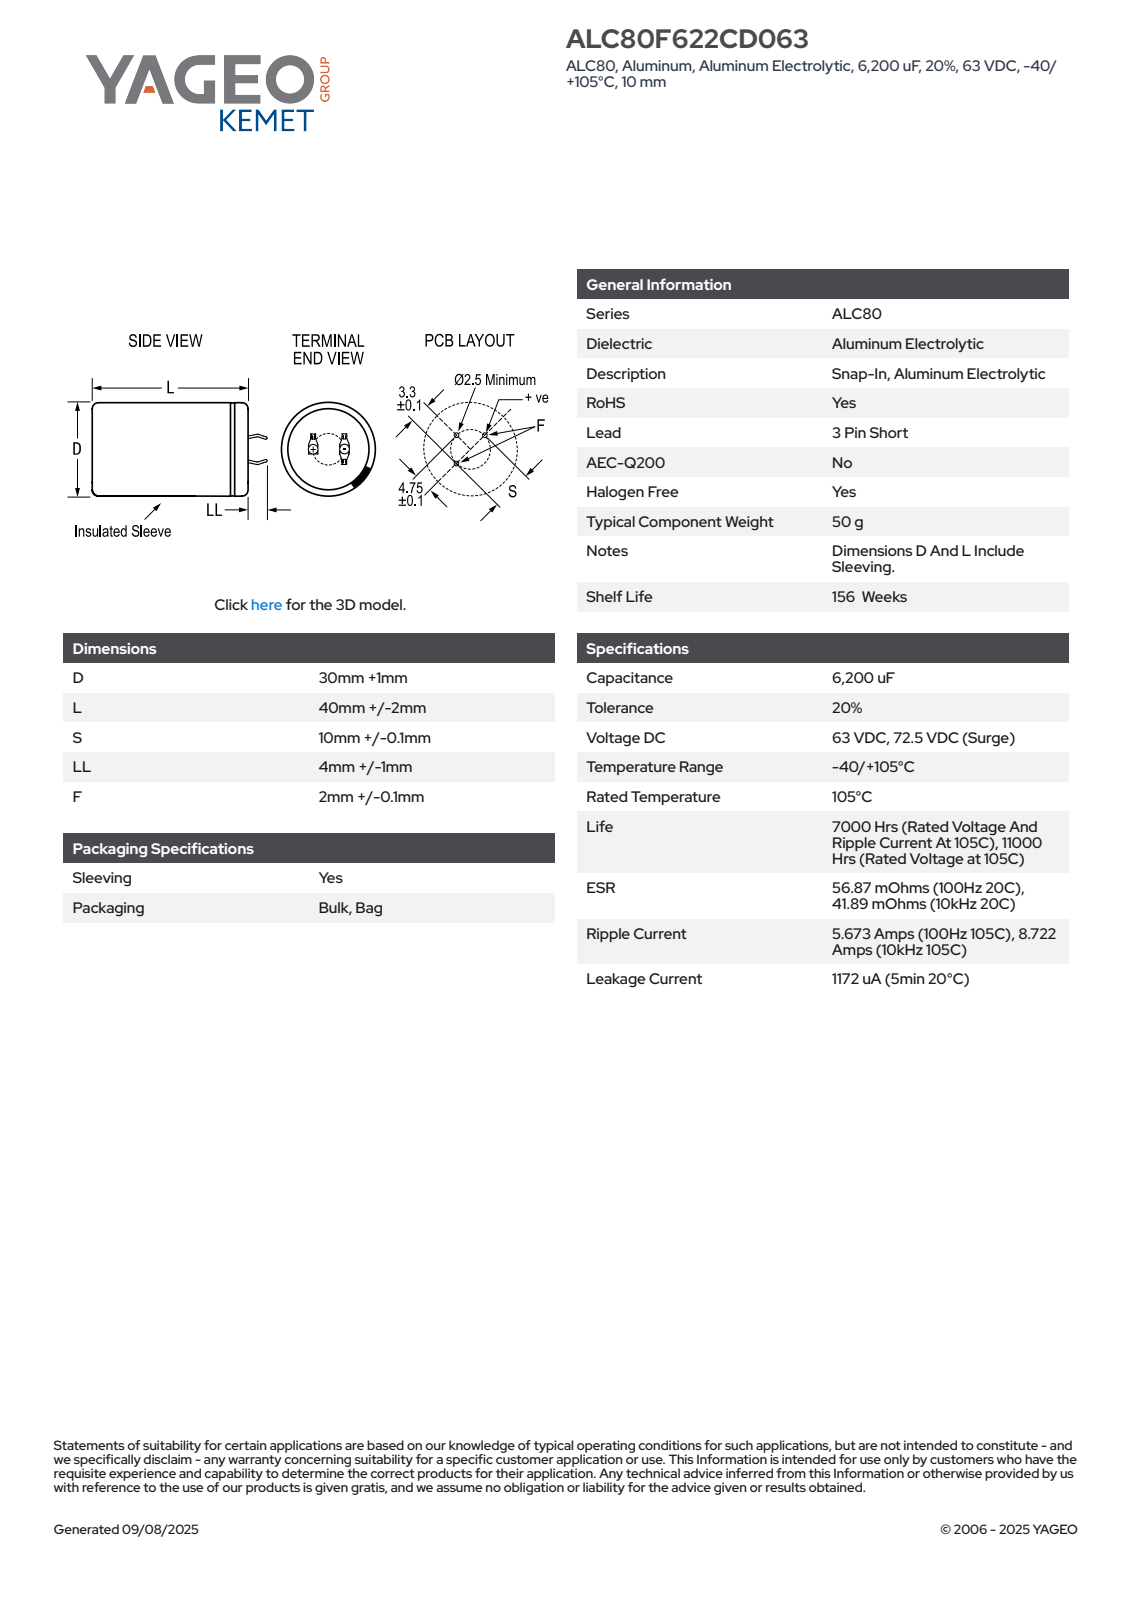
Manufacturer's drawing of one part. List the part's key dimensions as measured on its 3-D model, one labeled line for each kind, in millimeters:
Part name (STEP PRODUCT): CARS_K3P_30X40_D31L42S10LL5F2.1
STEP written by: SolidWorks 2014 (AUTOMOTIVE_DESIGN)
Units: millimetres
Bodies: 1 solid, 115 faces (61 planar, 15 cylindrical, 39 other)
Overall size (bounding box): 46.99 × 31 × 31
Volume: 31 367 mm³ · Surface area: 5 610 mm²
Round holes (diameter × count): ⌀27.43 ×1
Round bosses / shafts (diameter × count): ⌀31 ×1
Partial cylindrical surfaces — rounded edges, fillets, slot ends (radius × count): R15.49 ×1
Main face-to-face distances: 41.99, 42.49, 0.5, 0.6, 8.22, 0.59, 0.75, 1.35, 6.51, 8.97
